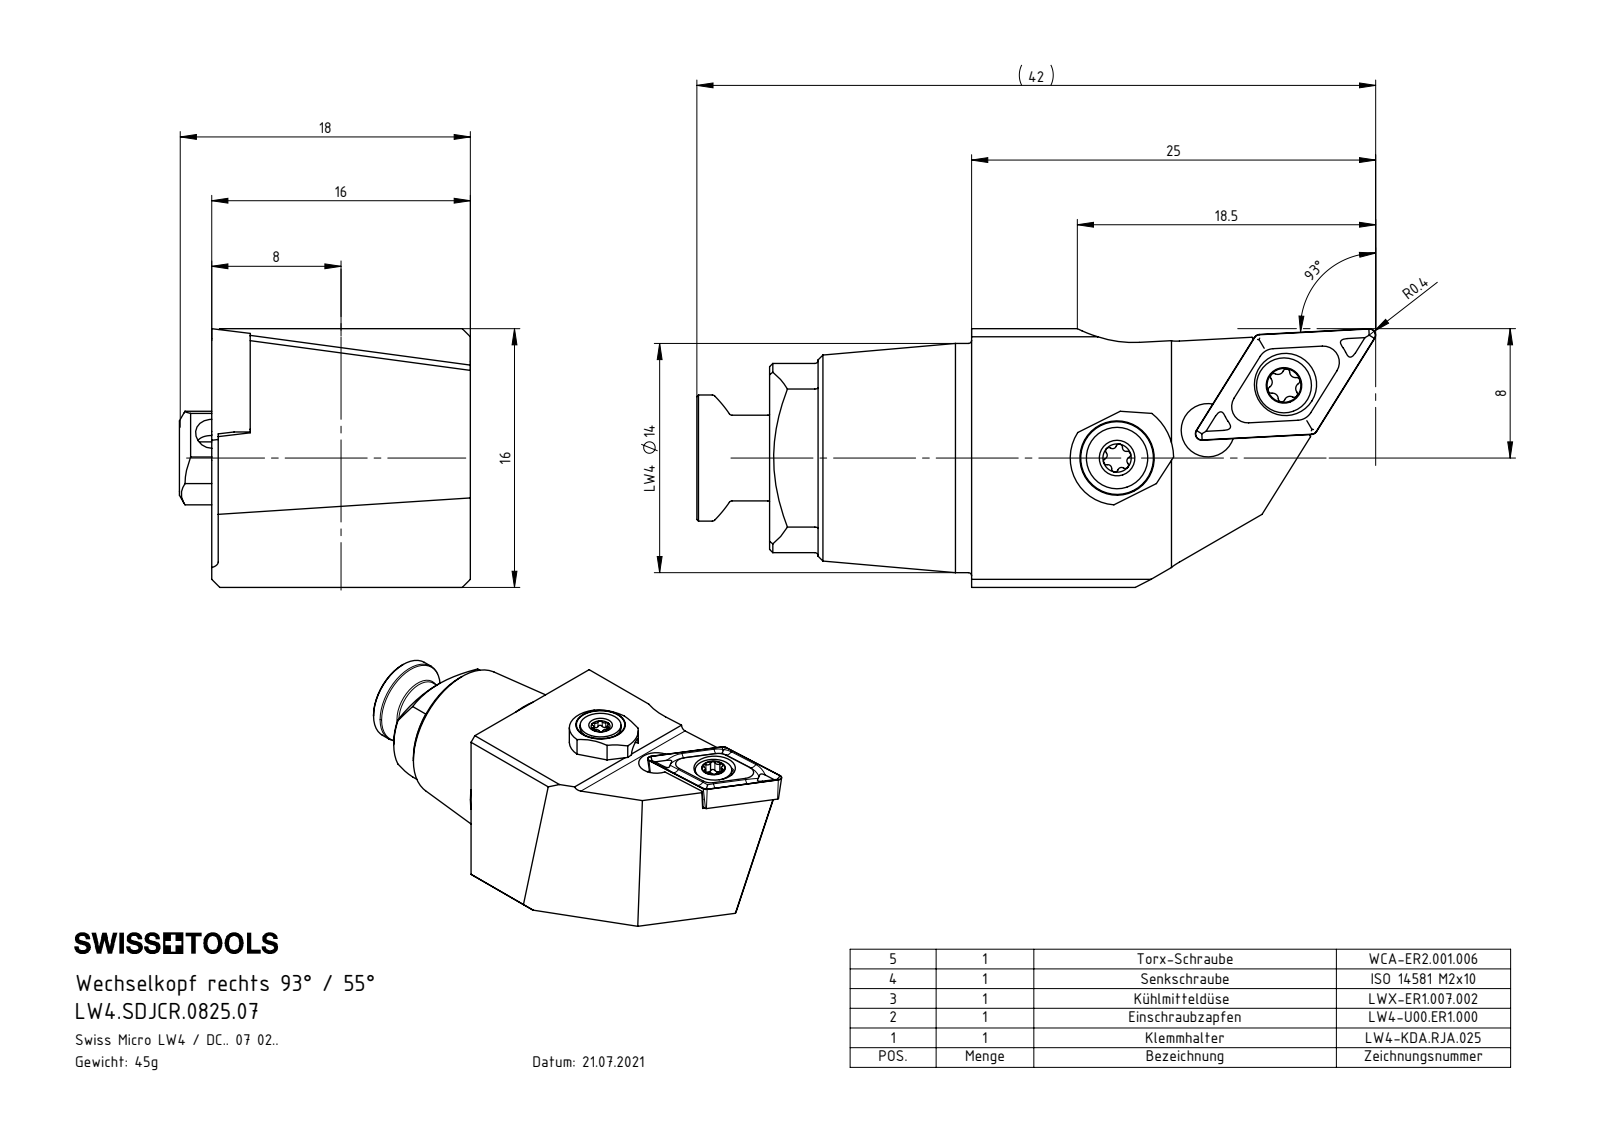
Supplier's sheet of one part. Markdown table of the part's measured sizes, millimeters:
| quantity | value |
| --- | --- |
| part name | ISO 14581 - M2x10; LW4-U00.ER1.000_B; DCMT070204; WCA-ER2.001.006_A (+3 more) |
| STEP written by | SolidWorks 2022 (CONFIG_CONTROL_DESIGN) |
| units | millimeters |
| bodies | 6 solids, 259 faces (70 planar, 81 cylindrical, 108 other) |
| overall size | 42 × 18 × 16 |
| volume | 5 812 mm³ |
| surface area | 3 361 mm² |
| round holes (diameter × count) | 3 × 2, 1.6 × 1, 2 × 1, 2.05 × 1, 2.5 × 1, 2.8 × 1, 3.3 × 1, 3.85 × 1, 5.5 × 1 |
| round bosses / shafts (diameter × count) | 14.17 × 1, 7.7 × 1, 6 × 1, 5.3 × 1, 5 × 1, 3.8 × 1, 3.4 × 1, 2.5 × 1 |
| partial cylindrical surfaces (radius × count) | 0.2 × 8, 0.21 × 6, 0.24 × 6, 0.36 × 4, 0.36 × 2, 0.5 × 1, 1 × 1, 2.9 × 1 |
| main face-to-face distances | 16, 13.62, 2.38, 15.6, 1.98, 0.4, 7.5, 2, 12.5, 4 |
| hole center spacings | 5.46, 5.57, 5.88, 11.26, 11.37 |
